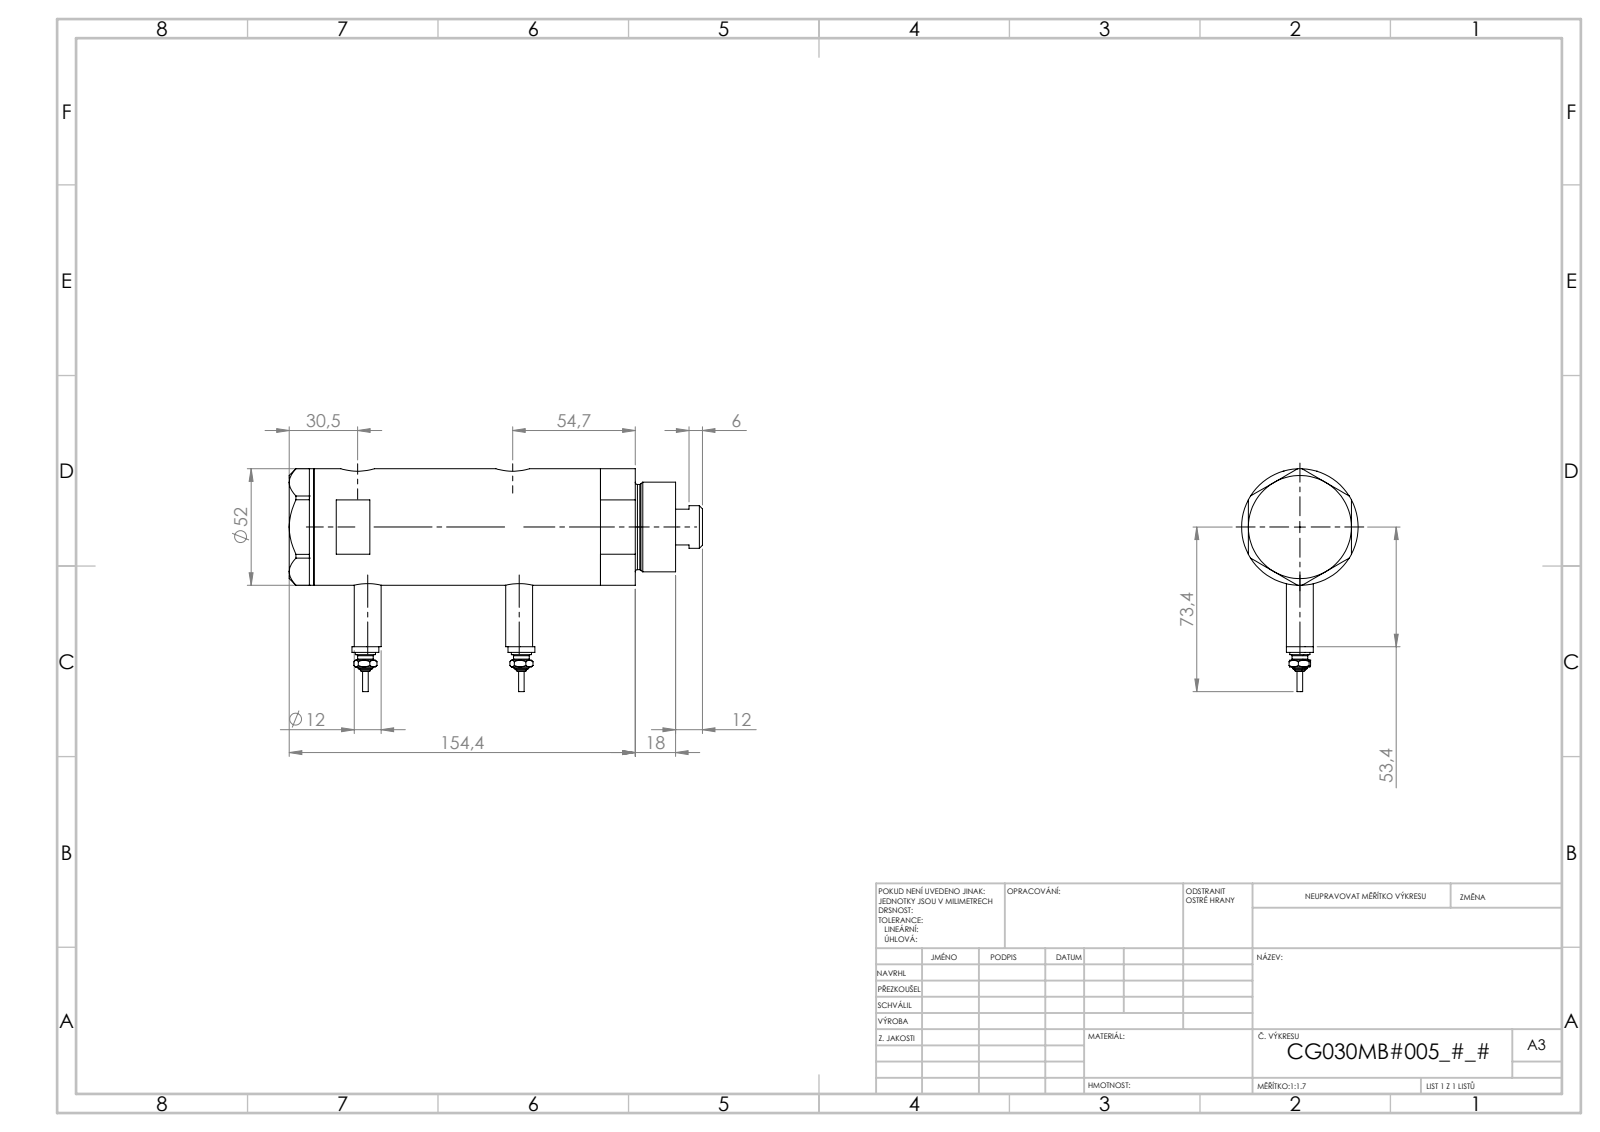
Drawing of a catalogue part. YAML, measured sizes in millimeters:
part_name: "V270CG_MIDDLE; V270CG_SWITCH; V270CG_BACK; V270CG_FRONT (+1 more)"
step_written_by: "SolidWorks 2019 (CONFIG_CONTROL_DESIGN)"
units: millimeters
bodies: {solids: 6, faces: 246, planar: 95, cylindrical: 77, other: 74}
overall_size: [154.02, 84.3, 52]
volume: 279030
surface_area: 68638
round_holes:
  - {diameter: 5, count: 2}
  - {diameter: 9.73, count: 2}
  - {diameter: 12.5, count: 2}
  - {diameter: 15, count: 2}
  - {diameter: 6.5, count: 1}
  - {diameter: 20, count: 1}
  - {diameter: 21.5, count: 1}
  - {diameter: 30, count: 1}
  - {diameter: 33, count: 1}
  - {diameter: 44, count: 1}
round_bosses_or_shafts:
  - {diameter: 12, count: 3}
  - {diameter: 9, count: 2}
  - {diameter: 7, count: 2}
  - {diameter: 4.34, count: 2}
  - {diameter: 2.4, count: 2}
  - {diameter: 52, count: 1}
  - {diameter: 40, count: 1}
  - {diameter: 38, count: 1}
face_to_face_distances: [58.56, 23.8, 34.76, 11, 34.8, 69.56, 46, 105.96, 94.96, 71.16]
hole_center_spacings: [2.9, 4.5, 31.75, 34.65, 36.25, 39.15, 2.89, 2.91]
